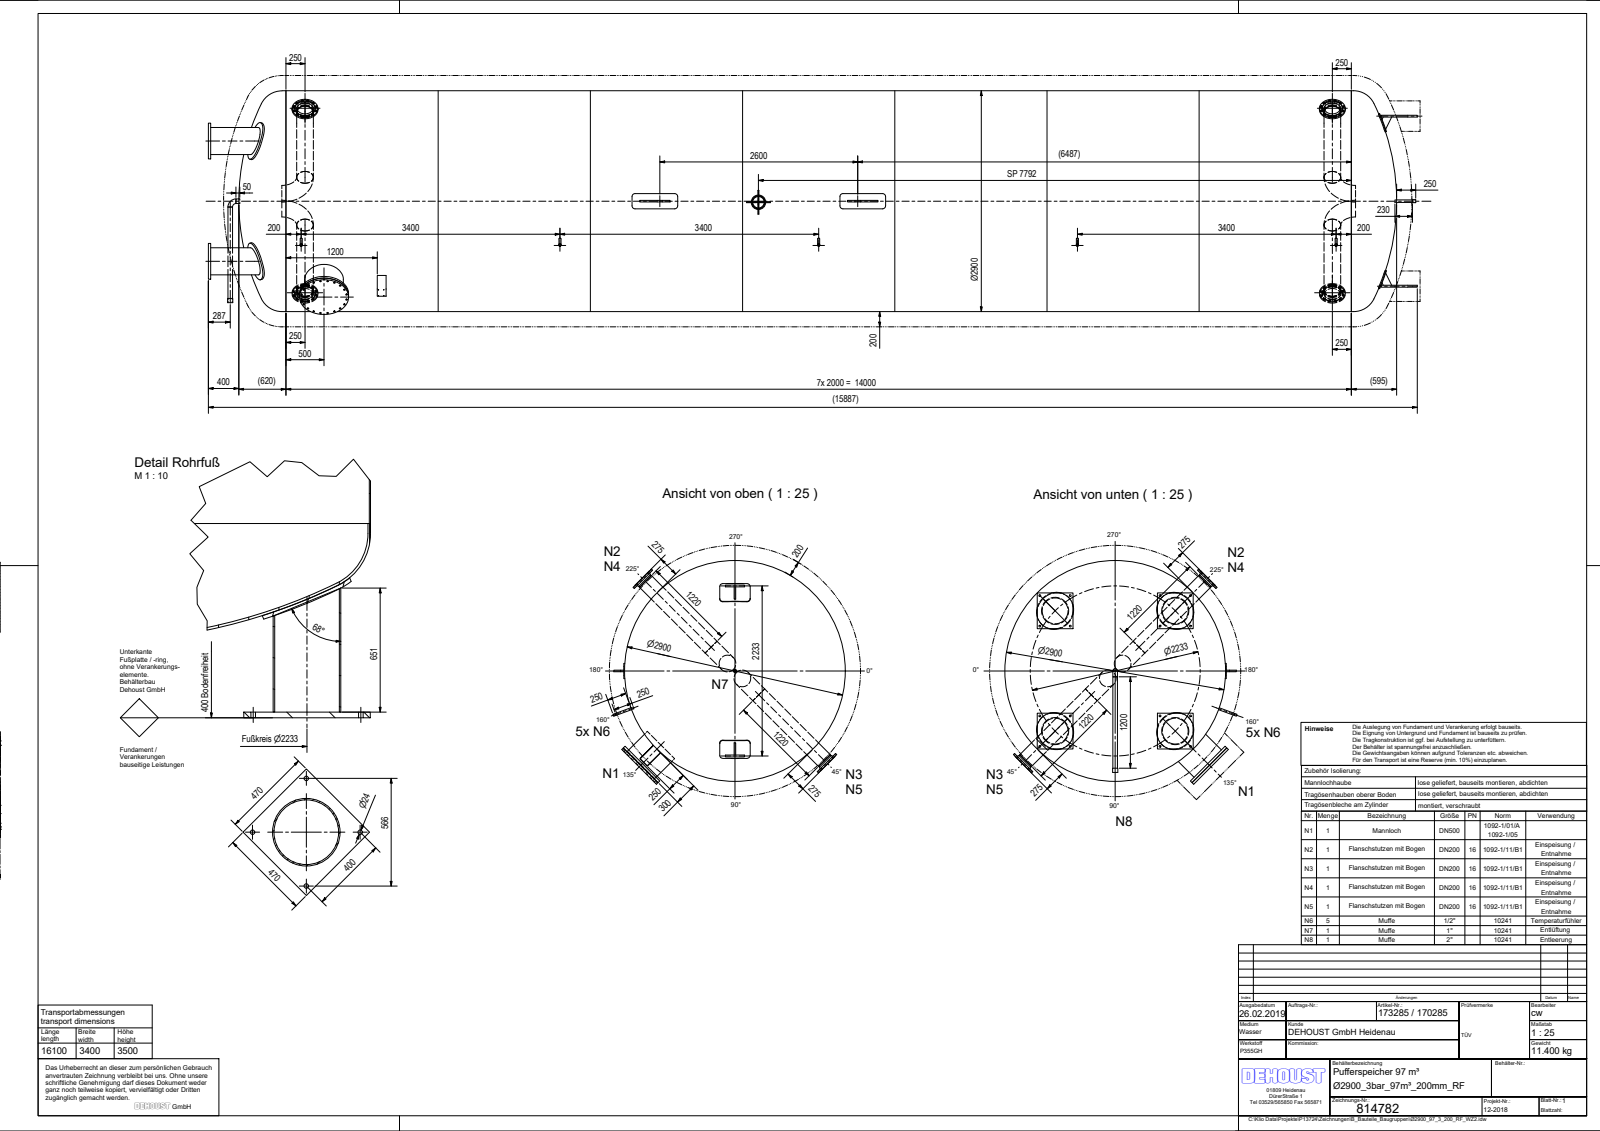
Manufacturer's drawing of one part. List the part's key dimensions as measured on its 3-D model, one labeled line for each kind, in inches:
Part name (STEP PRODUCT): Ø2900_97_3_200_RF_WZ2; Klöpper_Gew_Ø2900_7,5; Klöpper_Gew_Ø2900_13,0; Zyl_Ø2900_6x14000_2019 (+8 more)
STEP written by: Autodesk Inventor 2019 (AUTOMOTIVE_DESIGN)
Units: inches
Bodies: 58 solids, 457 faces (176 planar, 231 cylindrical, 50 other)
Overall size (bounding box): 625.46 × 120.157 × 115.646
Volume: 84 030 in³ · Surface area: 488 900 in²
Round holes (diameter × count): ⌀0.866 ×80, ⌀0.945 ×16, ⌀0.733 ×5, ⌀0.854 ×5, ⌀1.059 ×5, ⌀0.228 ×4, ⌀6.626 ×4, ⌀8.067 ×4, ⌀8.161 ×4, ⌀13.37 ×4, ⌀2.059 ×2, ⌀2.835 ×2
Round bosses / shafts (diameter × count): ⌀8.626 ×8, ⌀1.059 ×5, ⌀1.039 ×5, ⌀19.685 ×4, ⌀14 ×4, ⌀13.386 ×4, ⌀10.551 ×4, ⌀114.173 ×1
Partial cylindrical surfaces — rounded edges, fillets, slot ends (radius × count): R1.575 ×8, R1.654 ×8, R0.197 ×2, R0.394 ×2, R2.835 ×2, R4.921 ×1, R57.559 ×1
Main face-to-face distances: 23.622, 1.181, 298.927, 332.588, 297.746, 331.407, 33.661, 1.102, 258.76, 292.421
Hole centre spacings: 11.811, 5.807, 7.3, 3.695, 133.858, 13.885, 23.331, 267.717
